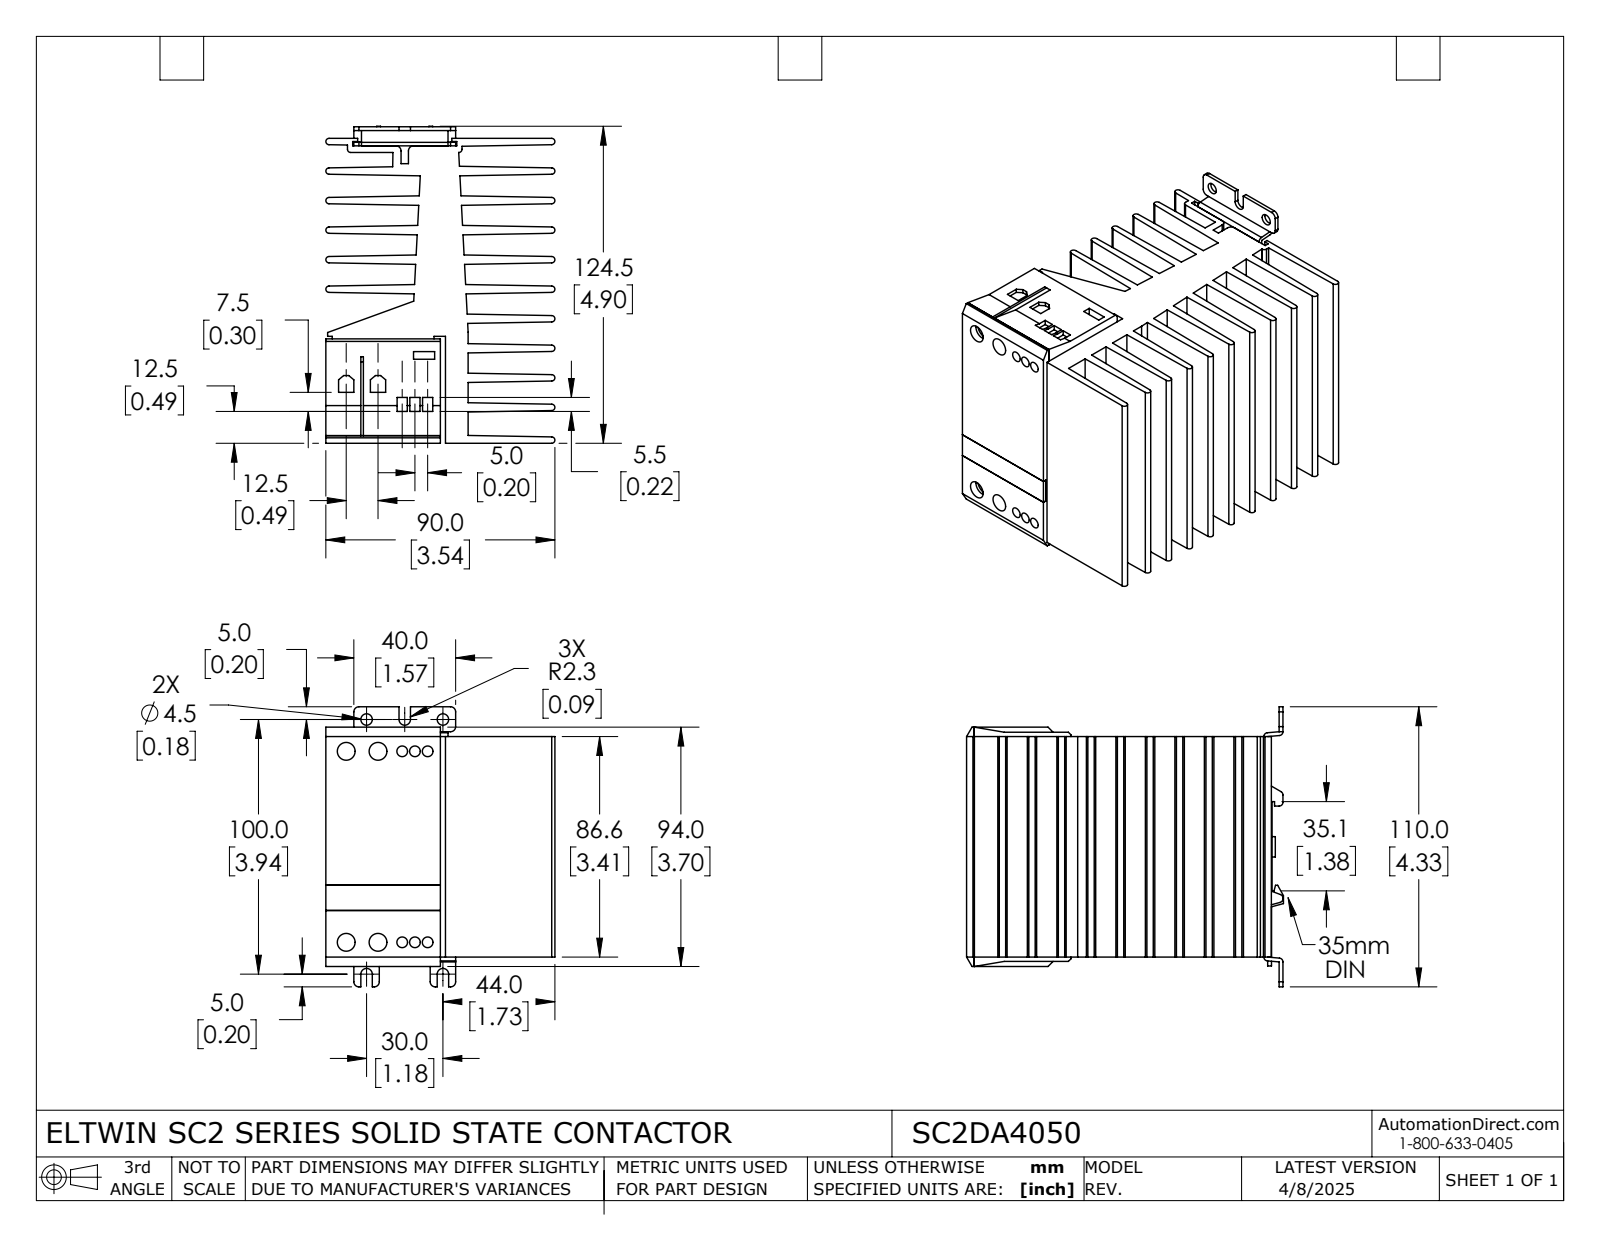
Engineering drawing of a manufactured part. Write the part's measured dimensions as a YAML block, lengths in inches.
part_name: "SC2DA4050"
step_written_by: "SolidWorks 2021 (AUTOMOTIVE_DESIGN)"
units: inches
bodies: {solids: 7, faces: 404, planar: 294, cylindrical: 110, other: 0}
overall_size: [4.902, 4.331, 3.543]
volume: 31.2
surface_area: 277.4
round_holes:
  - {diameter: 0.165, count: 6}
  - {diameter: 0.173, count: 6}
  - {diameter: 0.276, count: 4}
  - {diameter: 0.177, count: 2}
  - {diameter: 0.315, count: 2}
round_bosses_or_shafts:
  - {diameter: 0.315, count: 3}
partial_cylinders:
  - {radius: 0.049, count: 19}
  - {radius: 0.079, count: 18}
  - {radius: 0.059, count: 10}
  - {radius: 0.051, count: 4}
  - {radius: 0.089, count: 3}
face_to_face_distances: [0.457, 0.913, 1.37, 0.159, 0.3, 0.157, 1.827, 1.669, 1.828, 2.126]
hole_center_spacings: [2.953, 0.197, 2.959, 0.374, 0.394, 0.492, 0.571, 0.768]
